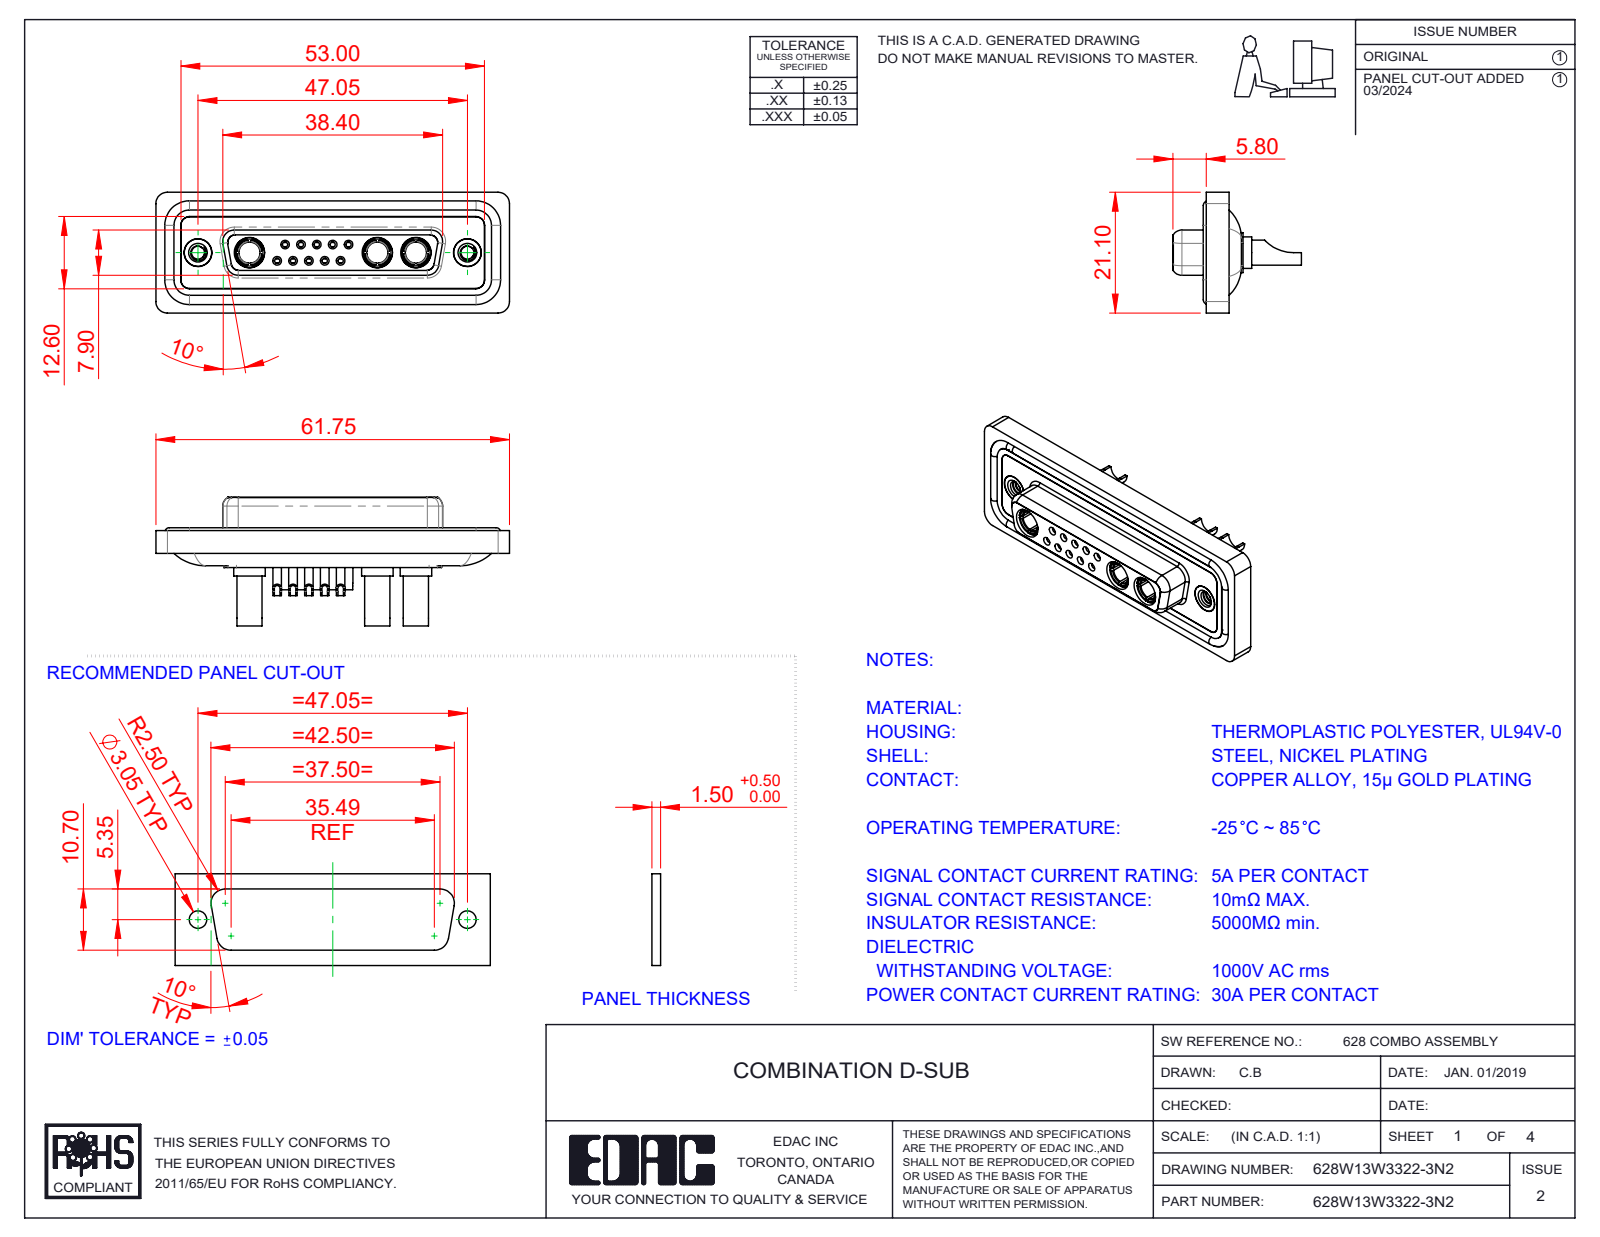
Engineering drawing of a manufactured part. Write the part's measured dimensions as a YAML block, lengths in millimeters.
part_name: "628Combo Shell Front_25 Contacts; 628Combo Contact Row 2_22; 628Combo Threaded Rivet_2; 628Combo Waterproof Housing_25 Contacts (+5 more)"
step_written_by: "SolidWorks 2023 (CONFIG_CONTROL_DESIGN)"
units: millimeters
bodies: {solids: 23, faces: 1176, planar: 371, cylindrical: 476, other: 329}
overall_size: [61.75, 22.45, 21.1]
volume: 8366
surface_area: 14136
round_holes:
  - {diameter: 0.9, count: 10}
  - {diameter: 1, count: 10}
  - {diameter: 1.1, count: 10}
  - {diameter: 1.5, count: 10}
  - {diameter: 2, count: 10}
  - {diameter: 1.6, count: 5}
  - {diameter: 1.7, count: 5}
  - {diameter: 4.85, count: 5}
  - {diameter: 3.5, count: 3}
  - {diameter: 3.7, count: 3}
  - {diameter: 5.3, count: 3}
  - {diameter: 2.26, count: 2}
round_bosses_or_shafts:
  - {diameter: 2.2, count: 10}
  - {diameter: 1.6, count: 9}
  - {diameter: 5.5, count: 3}
  - {diameter: 5.2, count: 3}
  - {diameter: 4.96, count: 3}
  - {diameter: 4.75, count: 3}
  - {diameter: 4.4, count: 3}
  - {diameter: 3.75, count: 3}
partial_cylinders:
  - {radius: 1.5, count: 22}
  - {radius: 2, count: 18}
  - {radius: 1.35, count: 8}
  - {radius: 1.6, count: 8}
  - {radius: 1, count: 6}
  - {radius: 0.25, count: 4}
  - {radius: 0.5, count: 4}
  - {radius: 0.6, count: 4}
face_to_face_distances: [0.4, 1.8, 7.45, 5.65, 0.5, 6.6, 7.05, 1.6, 2.9, 1.1]
hole_center_spacings: [3.16, 2.77, 5.03, 5.04, 5.54, 8.31, 7.49, 2.76]
